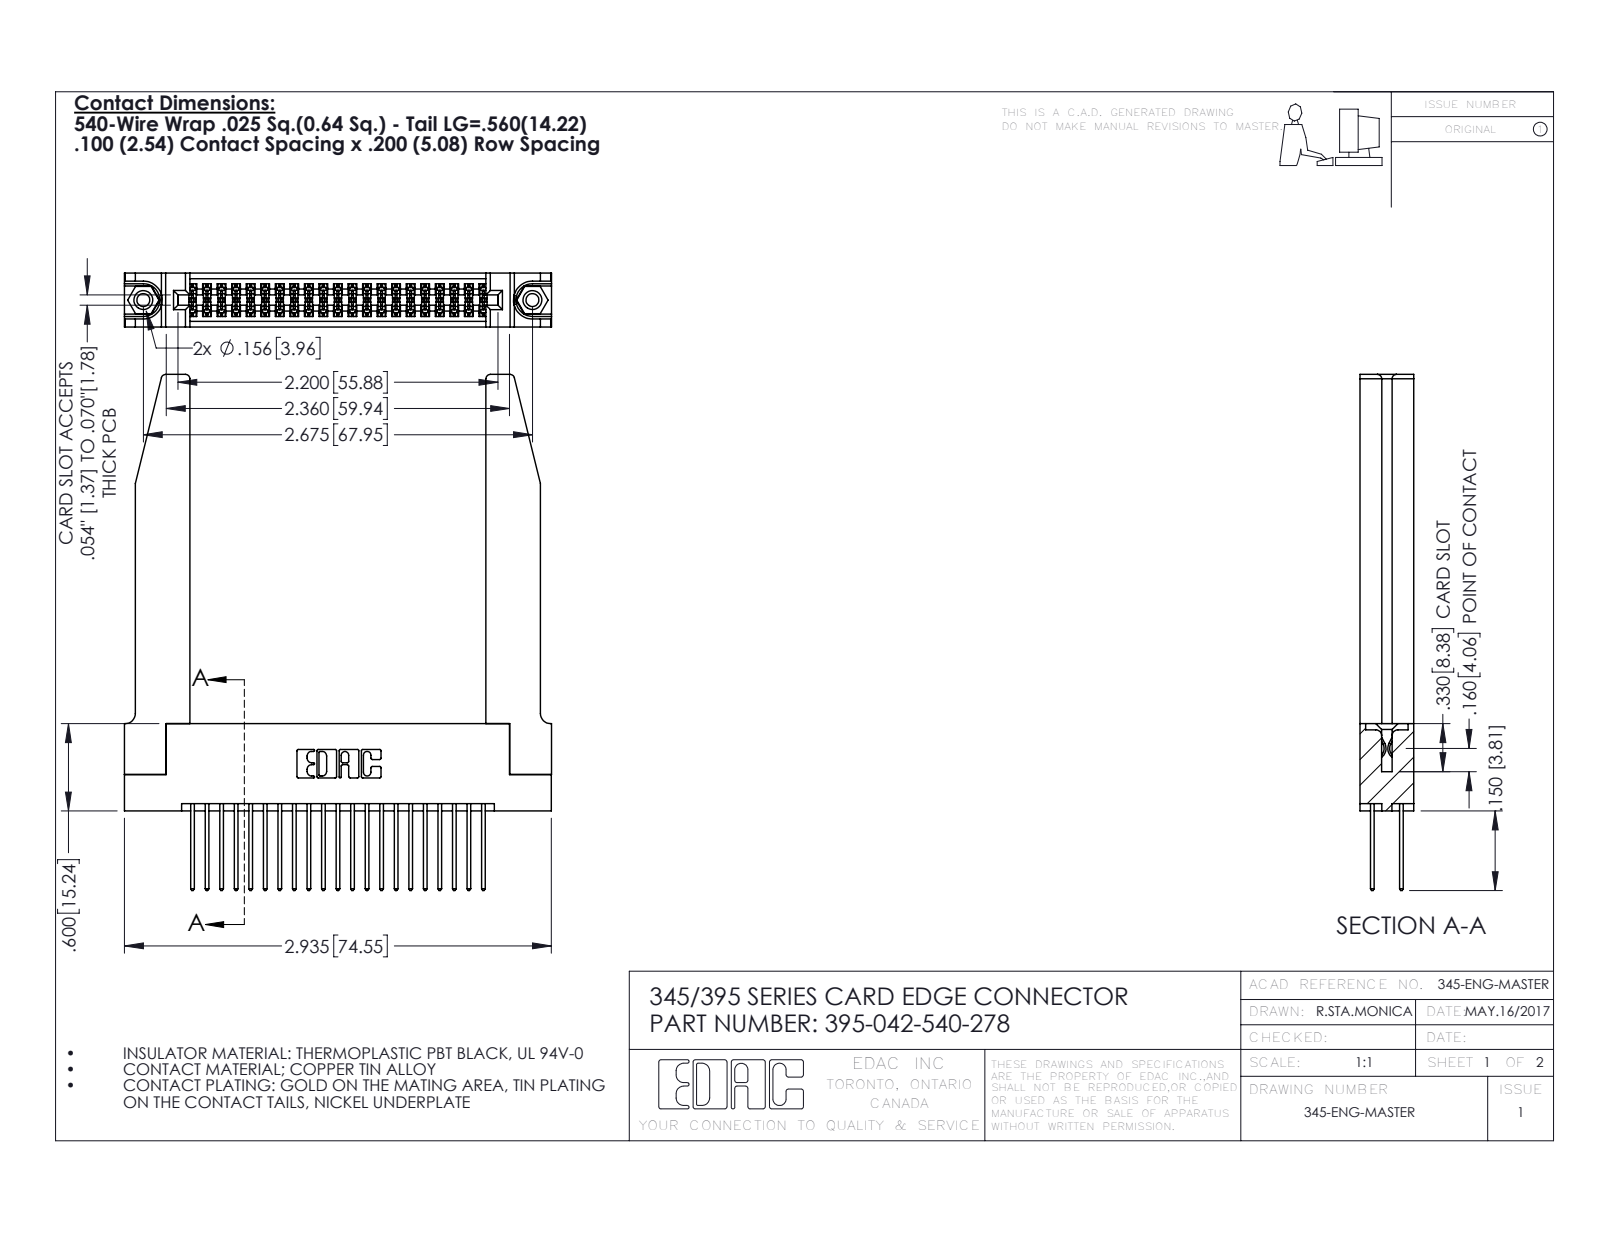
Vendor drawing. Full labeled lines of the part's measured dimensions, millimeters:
Part name (STEP PRODUCT): 345-292-001_345-293-140; 395-042-540-278; 345 Part_Flush Mounting Lugs - 0.156 Dia-TH; 345-250-001_345-250-001-102 (+1 more)
STEP written by: SolidWorks 2016 (CONFIG_CONTROL_DESIGN)
Units: millimetres
Bodies: 47 solids, 2460 faces (1608 planar, 800 cylindrical, 52 other)
Overall size (bounding box): 90.1 × 74.6 × 9.4
Volume: 15 000 mm³ · Surface area: 17 830 mm²
Round holes (diameter × count): ⌀2.3 ×2, ⌀3.2 ×2, ⌀4 ×2, ⌀1.6 ×1
Round bosses / shafts (diameter × count): ⌀3.9 ×2
Partial cylindrical surfaces — rounded edges, fillets, slot ends (radius × count): R0.2 ×63, R0.3 ×42, R0.3 ×22, R0.8 ×8, R0.2 ×6, R0.8 ×6, R0.7 ×3, R0.4 ×2
Main face-to-face distances: 9.4, 1.8, 7.6, 5.1, 2.5, 6.9, 0.6, 5.7, 3.8, 3.8
Hole centre spacings: 6.9, 62, 67.9
